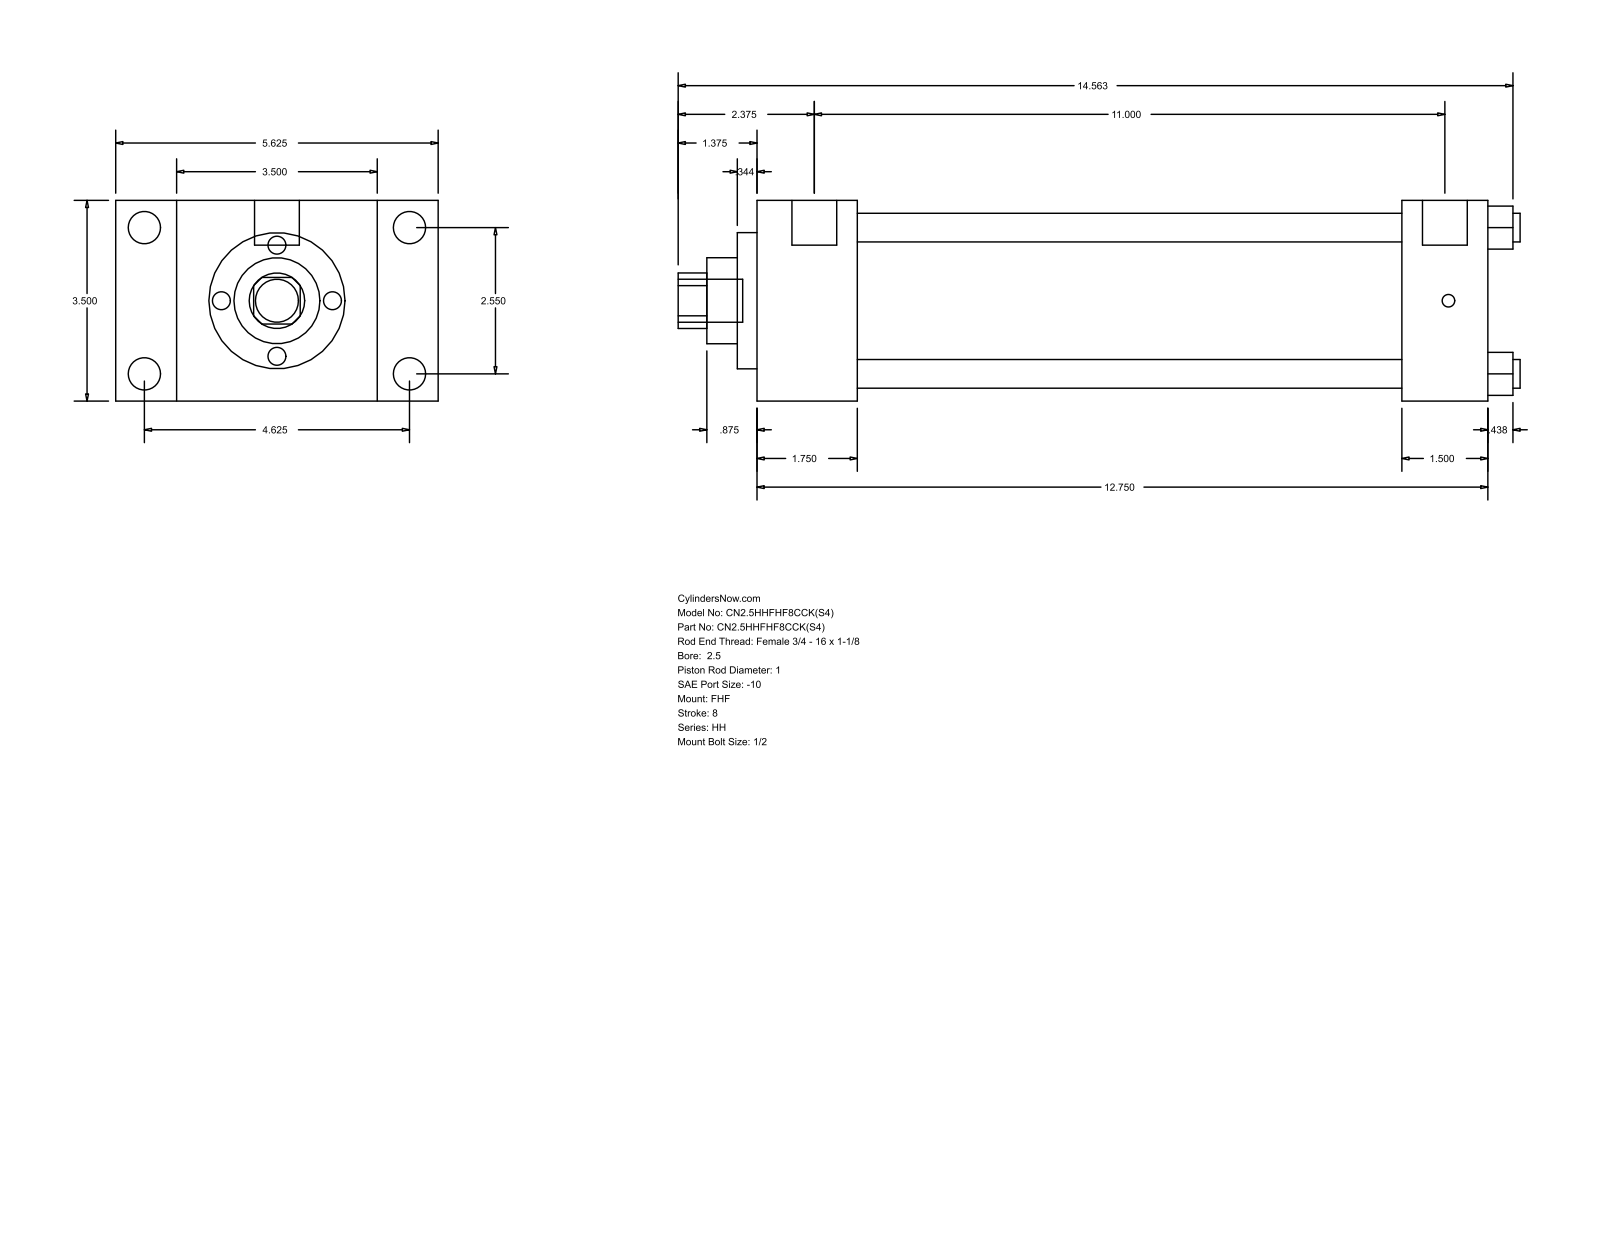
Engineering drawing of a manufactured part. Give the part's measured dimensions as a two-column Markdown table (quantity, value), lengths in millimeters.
| quantity | value |
| --- | --- |
| part name | HH_FHF__0250_1 |
| STEP written by | GSSL Pune (CONFIG_CONTROL_DESIGN) |
| units | millimeters |
| bodies | 0 solids, 90 faces (61 planar, 29 cylindrical, 0 other) |
| overall size | 373.06 × 142.88 × 88.9 |
| round holes (diameter × count) | 12.7 × 4, 25.4 × 1, 38.1 × 1, 60.33 × 1, 73.03 × 1 |
| round bosses / shafts (diameter × count) | 14.3 × 4, 5.56 × 4, 19.84 × 2, 19.05 × 1 |
| partial cylindrical surfaces (radius × count) | 12.29 × 1 |
| main face-to-face distances | 88.9, 44.46, 26.99, 115.89, 323.85, 279.39, 142.88, 285.76, 241.3, 38.09 |
| hole center spacings | 45.79, 64.76, 91.58 |
